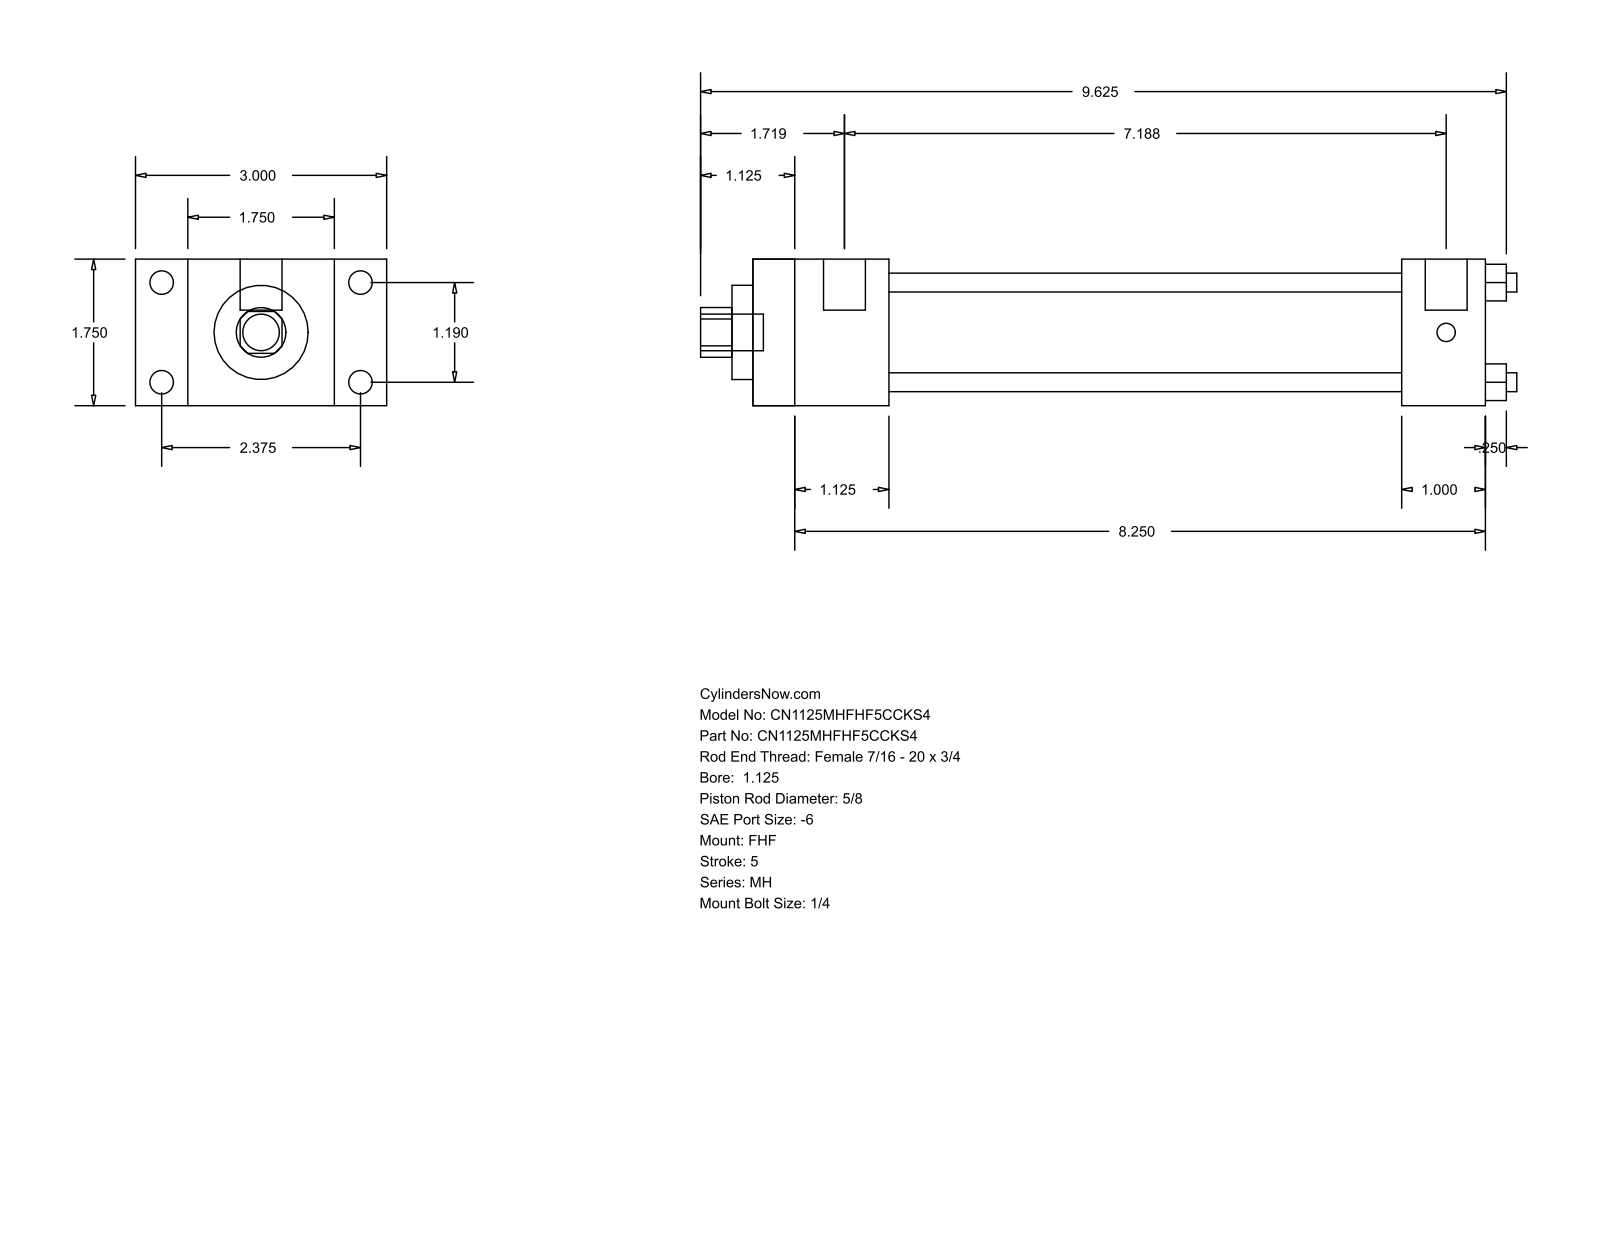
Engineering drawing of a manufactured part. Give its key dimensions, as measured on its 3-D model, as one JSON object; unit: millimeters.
{"part_name": "MH_FHF__0112_0.625", "step_written_by": "GSSL Pune (CONFIG_CONTROL_DESIGN)", "units": "millimeters", "bodies": {"solids": 0, "faces": 88, "planar": 60, "cylindrical": 28, "other": 0}, "overall_size": [247.65, 76.2, 44.45], "round_holes": [[5.71, 4], [15.88, 1], [28.57, 1], [34.92, 1]], "round_bosses_or_shafts": [[7.14, 4], [5.56, 4], [12.7, 2], [11.11, 1]], "partial_cylinders_radius": [[7.54, 1]], "face_to_face_distances": [44.46, 15.87, 60.33, 41.27, 76.2, 222.24, 180.97, 196.84, 155.57, 25.4], "hole_center_spacings": [21.37, 30.22, 42.74]}
